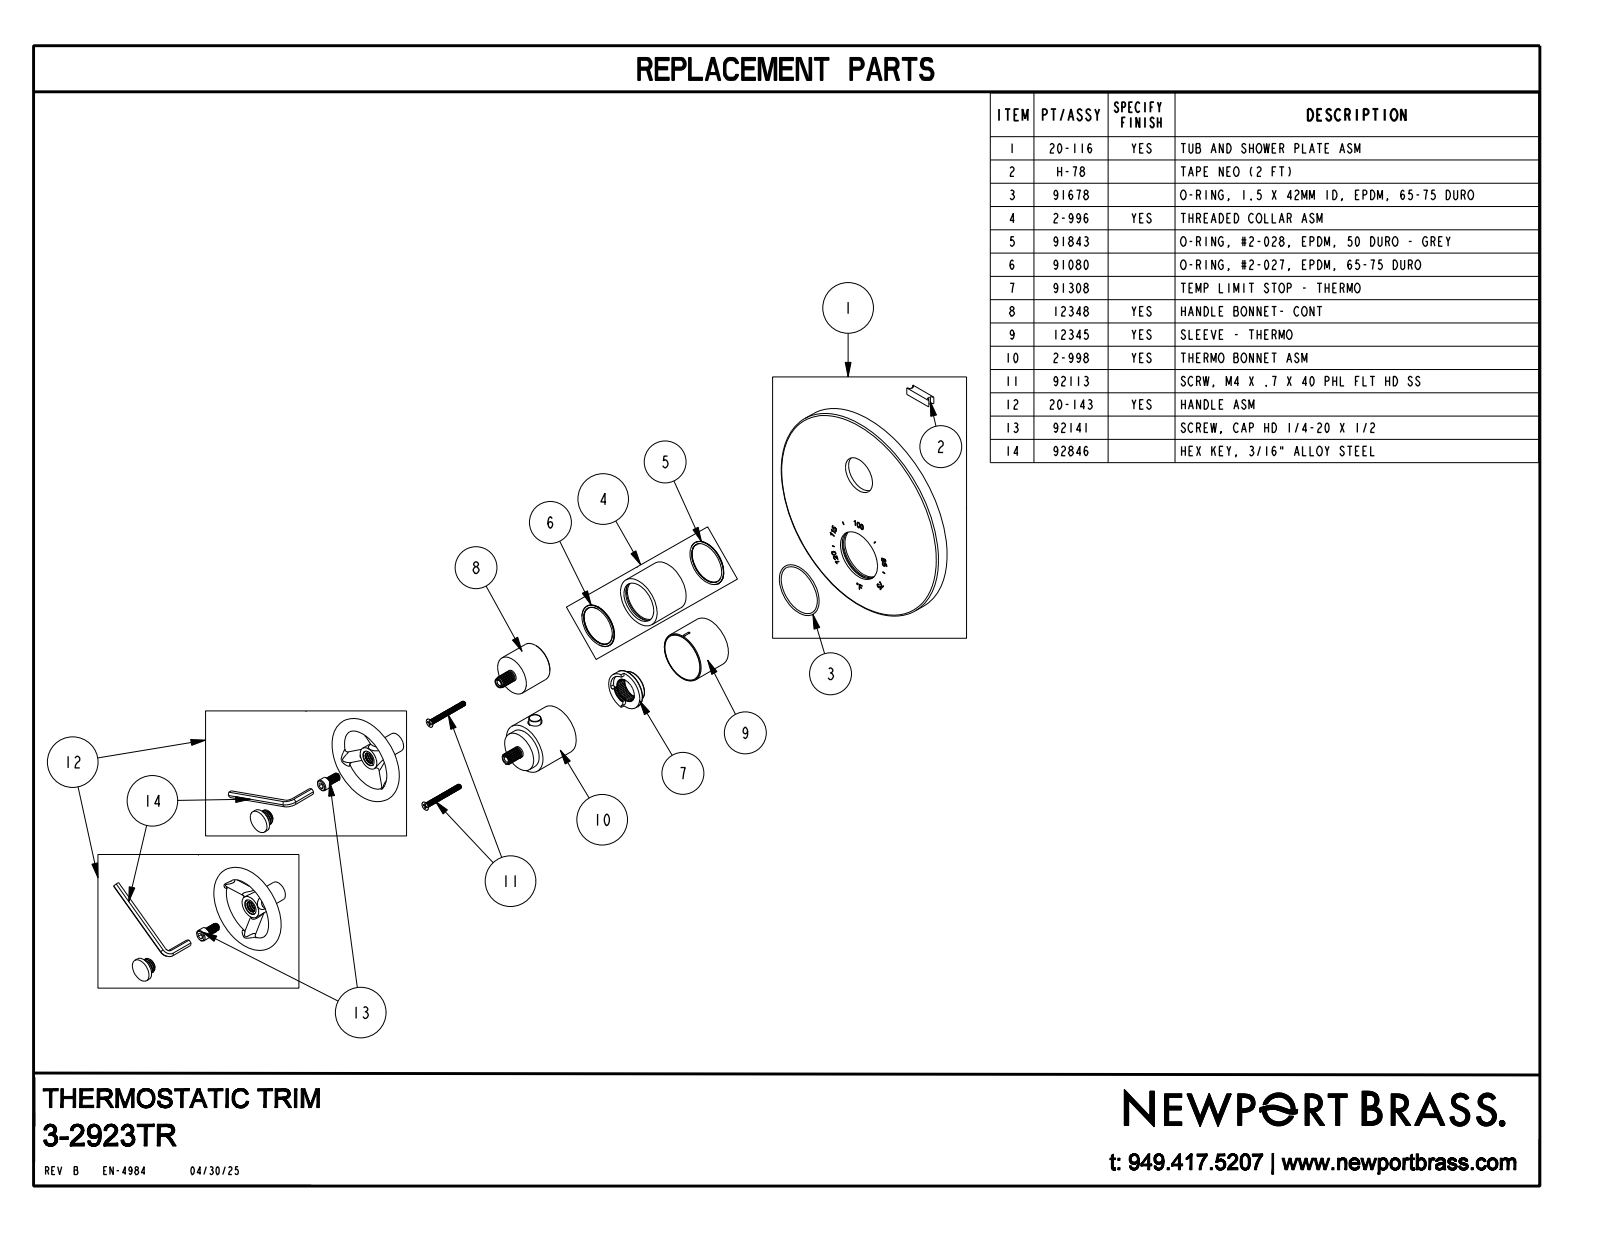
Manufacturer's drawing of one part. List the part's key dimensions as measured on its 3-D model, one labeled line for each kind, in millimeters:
Part name (STEP PRODUCT): 12347; 91678; 20-116_ASM; 12368 (+8 more)
STEP written by: PRO/ENGINEER BY PARAMETRIC TECHNOLOGY CORPORATION, 2014000 (CONFIG_CONTROL_DESIGN)
Units: millimetres
Bodies: 21 solids, 1721 faces (621 planar, 555 cylindrical, 545 other)
Overall size (bounding box): 180.1 × 180.1 × 101.1
Volume: 182 400 mm³ · Surface area: 128 900 mm²
Round holes (diameter × count): ⌀4.8 ×2, ⌀4.8 ×2, ⌀6.7 ×2, ⌀7 ×2, ⌀9.1 ×2, ⌀10.2 ×2, ⌀10.7 ×2, ⌀13 ×2, ⌀1.6 ×1, ⌀2 ×1, ⌀2.5 ×1, ⌀3.2 ×1
Round bosses / shafts (diameter × count): ⌀8.9 ×6, ⌀4 ×3, ⌀42 ×2, ⌀19.1 ×2, ⌀16 ×2, ⌀13 ×2, ⌀13 ×2, ⌀12.4 ×2
Partial cylindrical surfaces — rounded edges, fillets, slot ends (radius × count): R1 ×2, R1.9 ×2, R2.1 ×2, R3.2 ×2, R4.2 ×2, R4.3 ×2, R4.7 ×2, R13.9 ×1
Main face-to-face distances: 2, 4.4, 6.4, 7.1, 1.6, 2.8, 3.6, 54.5, 4.7, 7.5
Hole centre spacings: 14.1, 14.1, 25.9, 29, 29.1, 40, 40, 40
